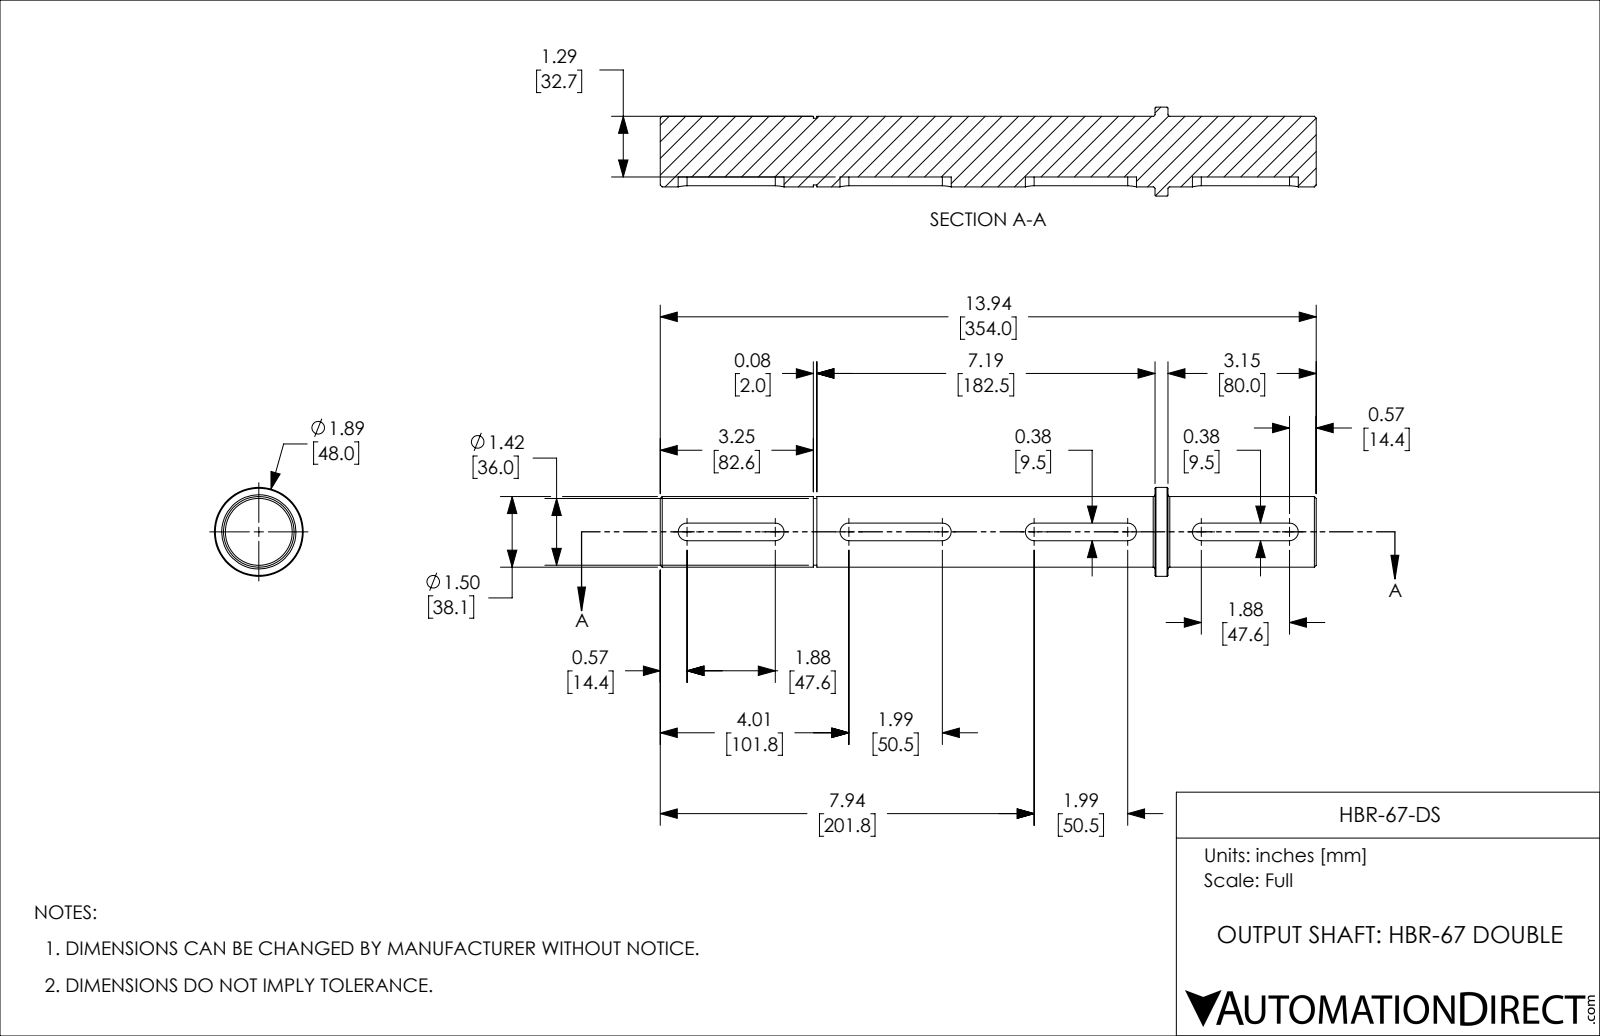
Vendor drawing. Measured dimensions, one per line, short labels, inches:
name: HBR-67-DS
written by: SolidWorks 2018 (AUTOMOTIVE_DESIGN)
unit: in
bodies: 1 solid, 52 faces (18 planar, 22 cylindrical, 12 other)
size: 13.938 × 1.89 × 1.89
volume: 24.21 in³; area: 75.27 in²
bosses: 1× ⌀1.89, 1× ⌀1.5, 1× ⌀1.417
rounds: 7× R0.188, 1× R0.187
face distances: 13.938, 0.375, 10.512, 3.426, 10.788, 0.276, 3.15, 3.327, 7.185, 7.461
